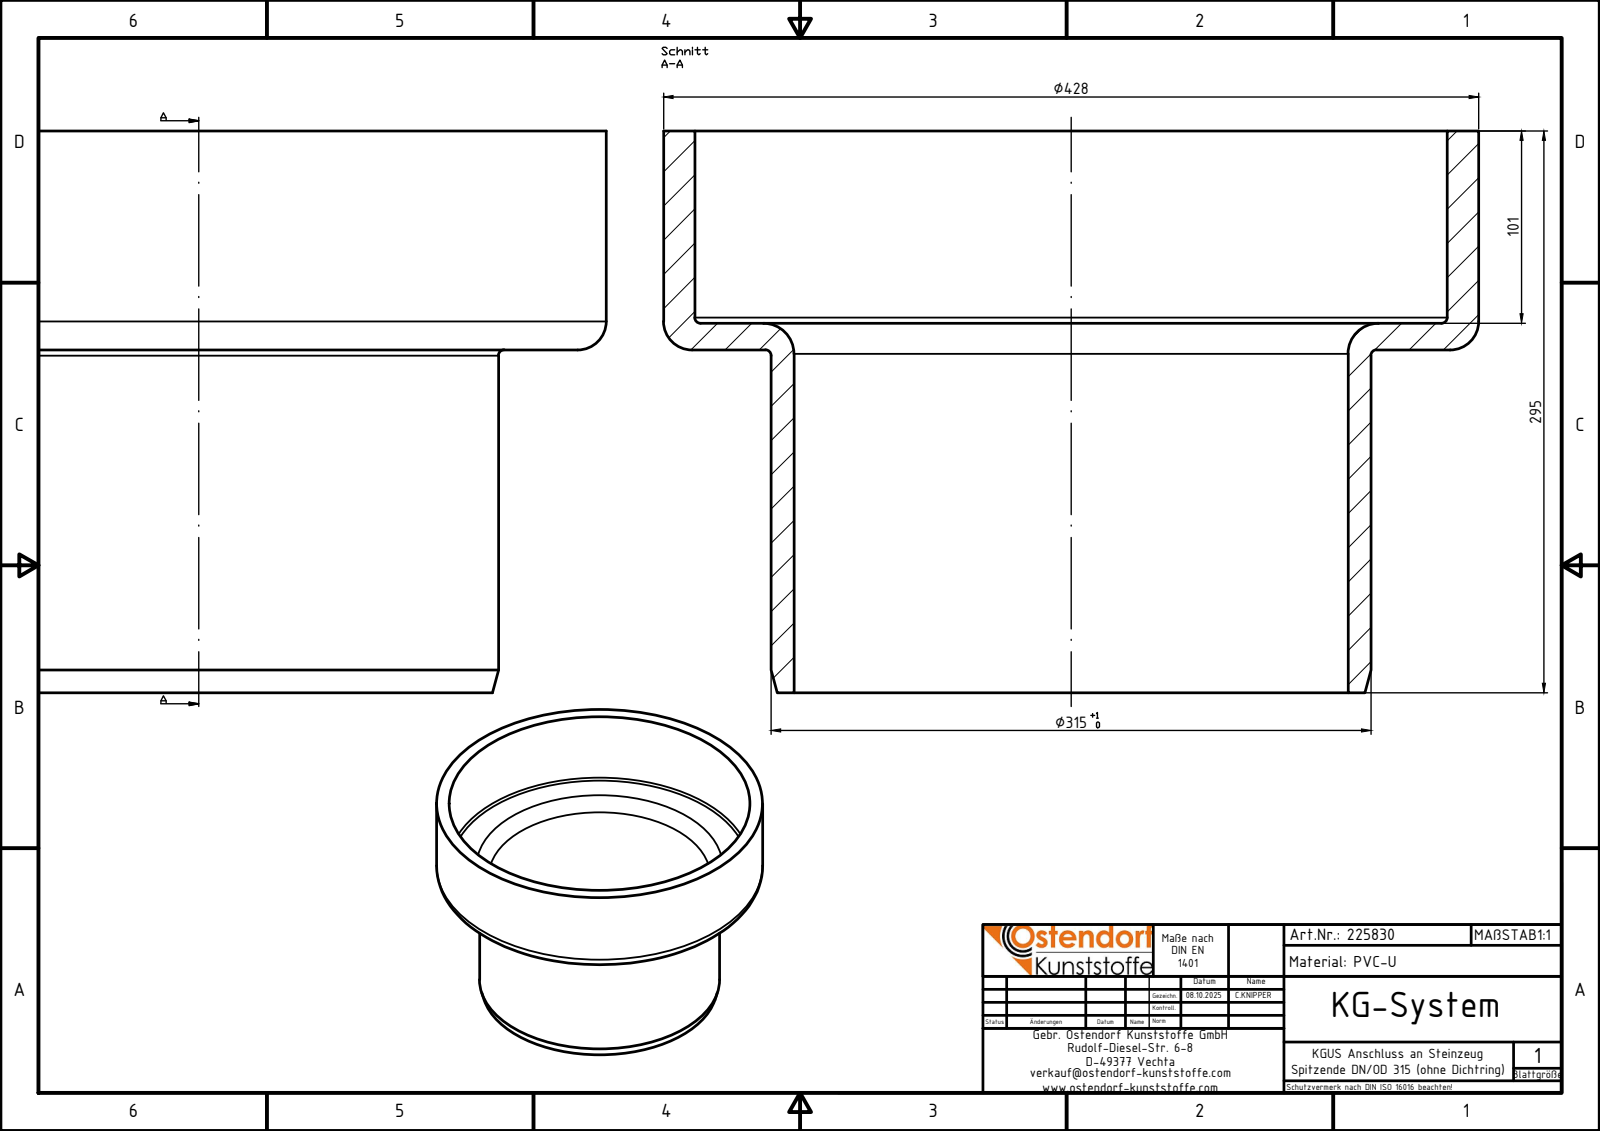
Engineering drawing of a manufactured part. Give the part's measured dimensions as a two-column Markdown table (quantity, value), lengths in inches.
| quantity | value |
| --- | --- |
| part name | 225830z |
| STEP written by | Autodesk Inventor 2024 (AUTOMOTIVE_DESIGN) |
| units | inches |
| bodies | 1 solid, 13 faces (4 planar, 4 cylindrical, 5 other) |
| overall size | 16.85 × 16.85 × 11.614 |
| volume | 315.1 in³ |
| surface area | 1 193 in² |
| round holes (diameter × count) | 11.457 × 1, 15.551 × 1 |
| round bosses / shafts (diameter × count) | 16.85 × 1, 12.402 × 1 |
| main face-to-face distances | 0.551, 4.528, 3.976, 7.087, 7.638, 11.614 |
